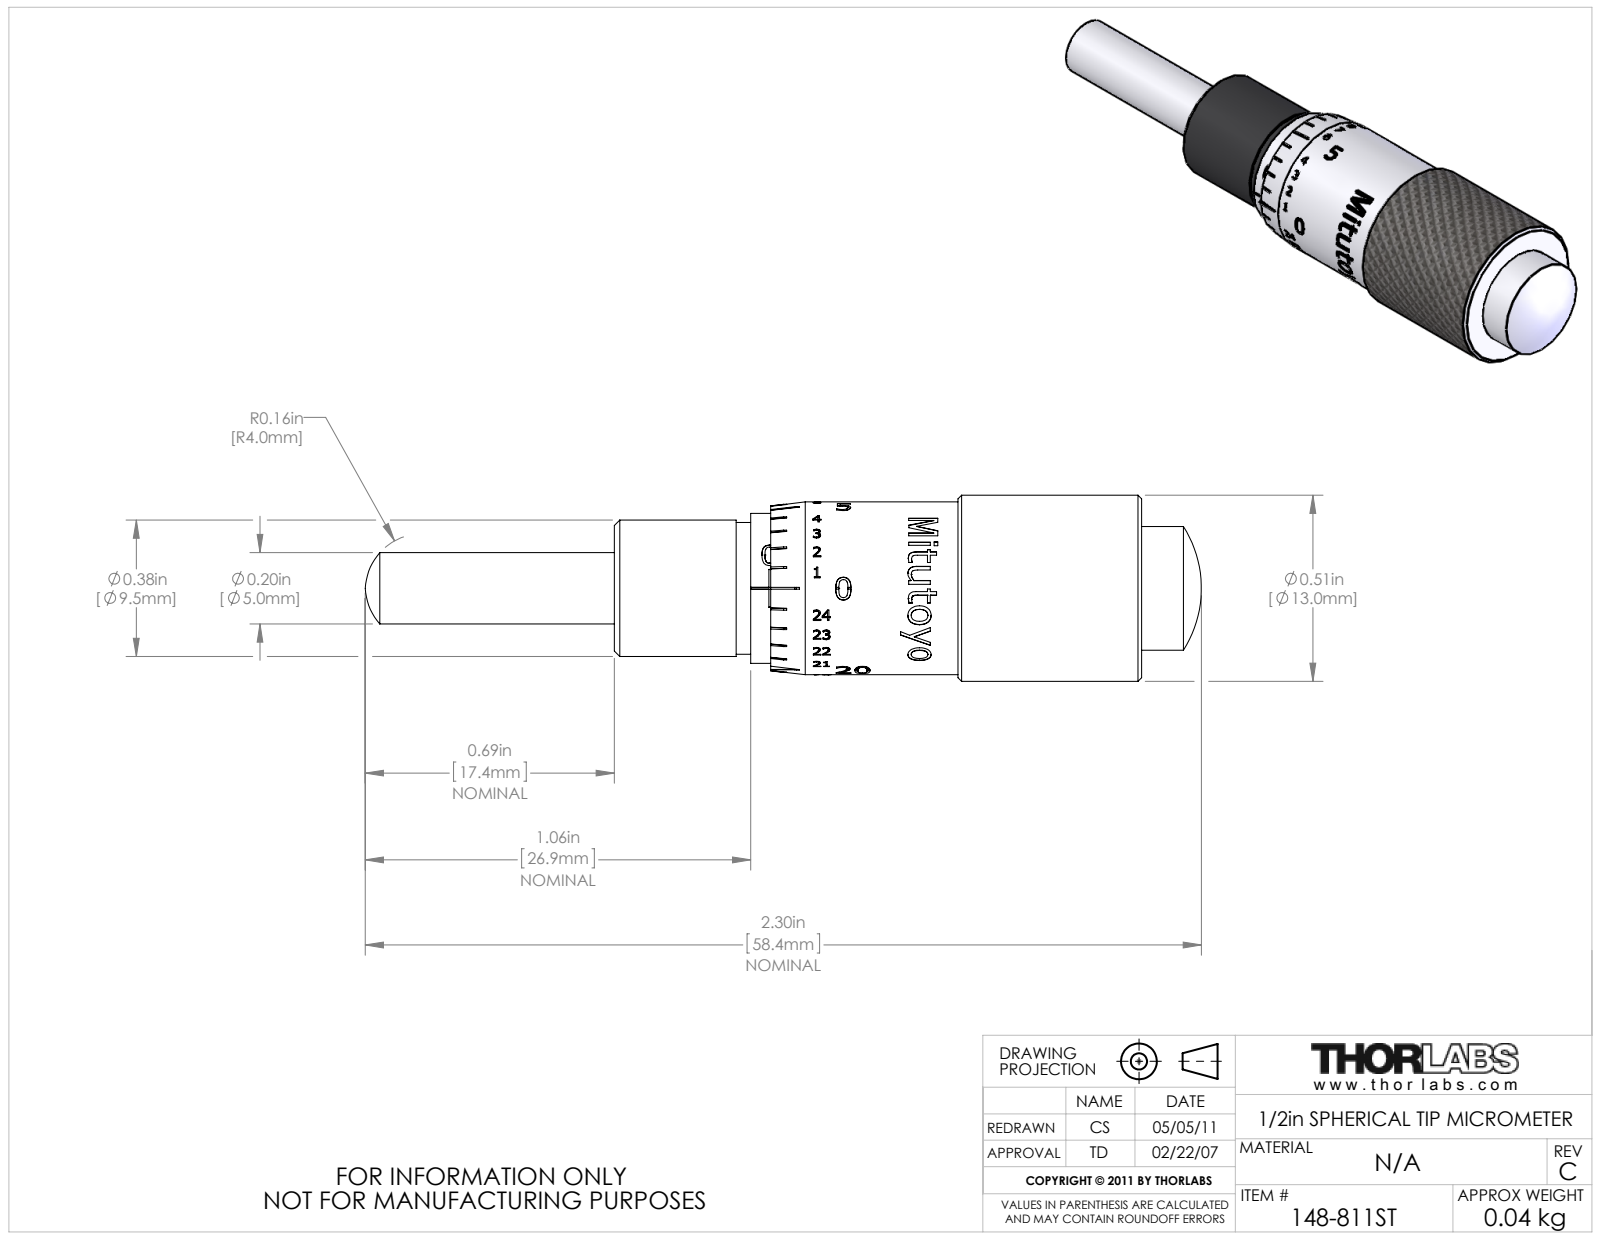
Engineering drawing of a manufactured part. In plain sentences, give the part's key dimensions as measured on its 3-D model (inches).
The part is named "13430-E0W". Its 3-D file was written by "SolidWorks 2012 (AUTOMOTIVE_DESIGN)". It is 2 solids with 1171 faces: 599 planar, 108 cylindrical and 464 other. Overall it measures 2.299 by 0.512 by 0.512 inches. Its volume is 0.263 cubic inches and its surface area 6.894 square inches. Round holes: 1 of diameter 0.197, 1 of diameter 0.42. Round bosses or shafts: 1 of diameter 0.512, 1 of diameter 0.475, 1 of diameter 0.413, 1 of diameter 0.386, 1 of diameter 0.375, 1 of diameter 0.362, 1 of diameter 0.34, 1 of diameter 0.196. Partial cylindrical surfaces (rounded edges, fillets, slot ends): 1 of radius 0.205, 1 of radius 0.232, 1 of radius 0.235, 1 of radius 0.236. The main face-to-face distances are 0.188, 0.037, 0.225, 1.45, 1.262, 1.225, 1.075, 0.887, 0.85, 0.375.
